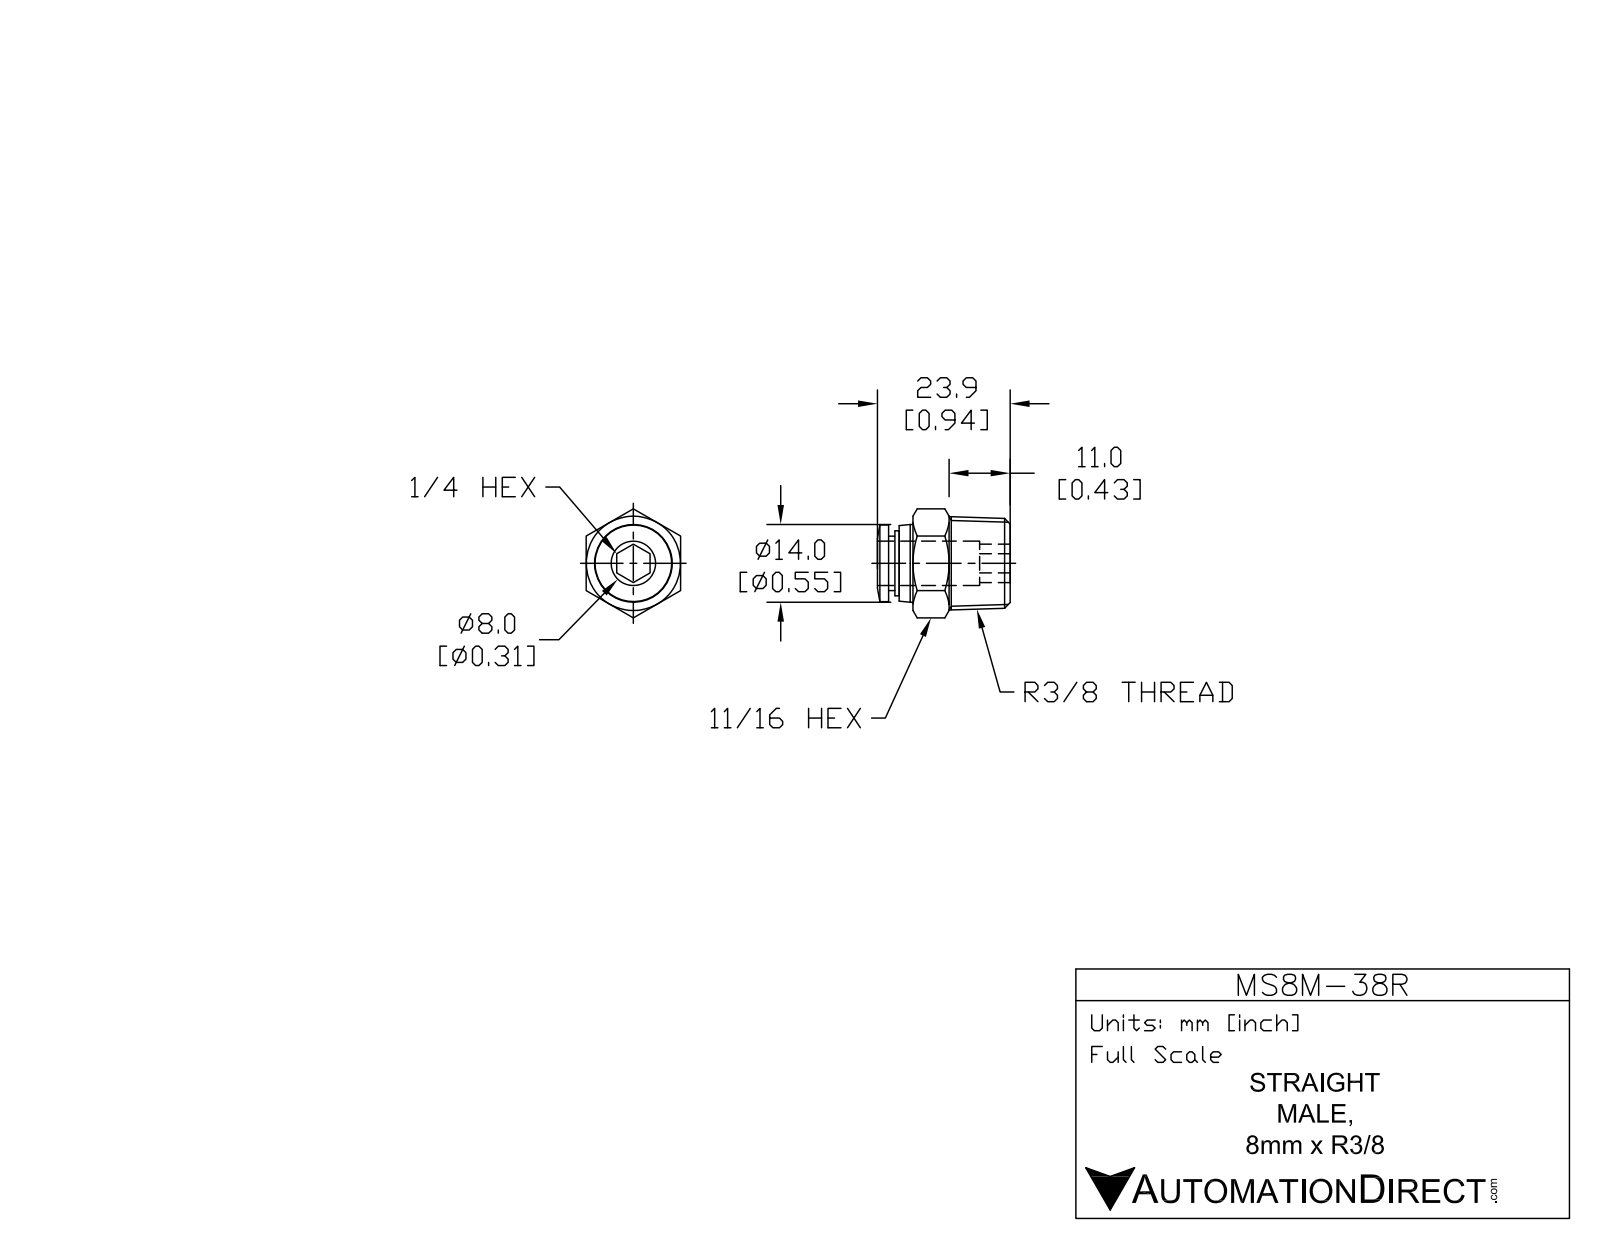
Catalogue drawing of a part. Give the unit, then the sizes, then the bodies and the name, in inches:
Units: inches
Overall size (bounding box): 0.941 × 0.773 × 0.669
Round holes (diameter × count): ⌀0.276 ×1, ⌀0.327 ×1
Round bosses / shafts (diameter × count): ⌀0.551 ×1, ⌀0.543 ×1, ⌀0.461 ×1, ⌀0.386 ×1
Main face-to-face distances: 0.669, 0.862, 0.689, 0.173, 0.787, 0.098, 0.075, 0.817, 0.128, 0.03
Volume: 0.217 in³ · Surface area: 3.54 in²
Bodies: 1 solid, 50 faces (14 planar, 12 cylindrical, 24 other)
Part name (STEP PRODUCT): MS8M-38R
STEP written by: SolidWorks 2015 (AUTOMOTIVE_DESIGN)
